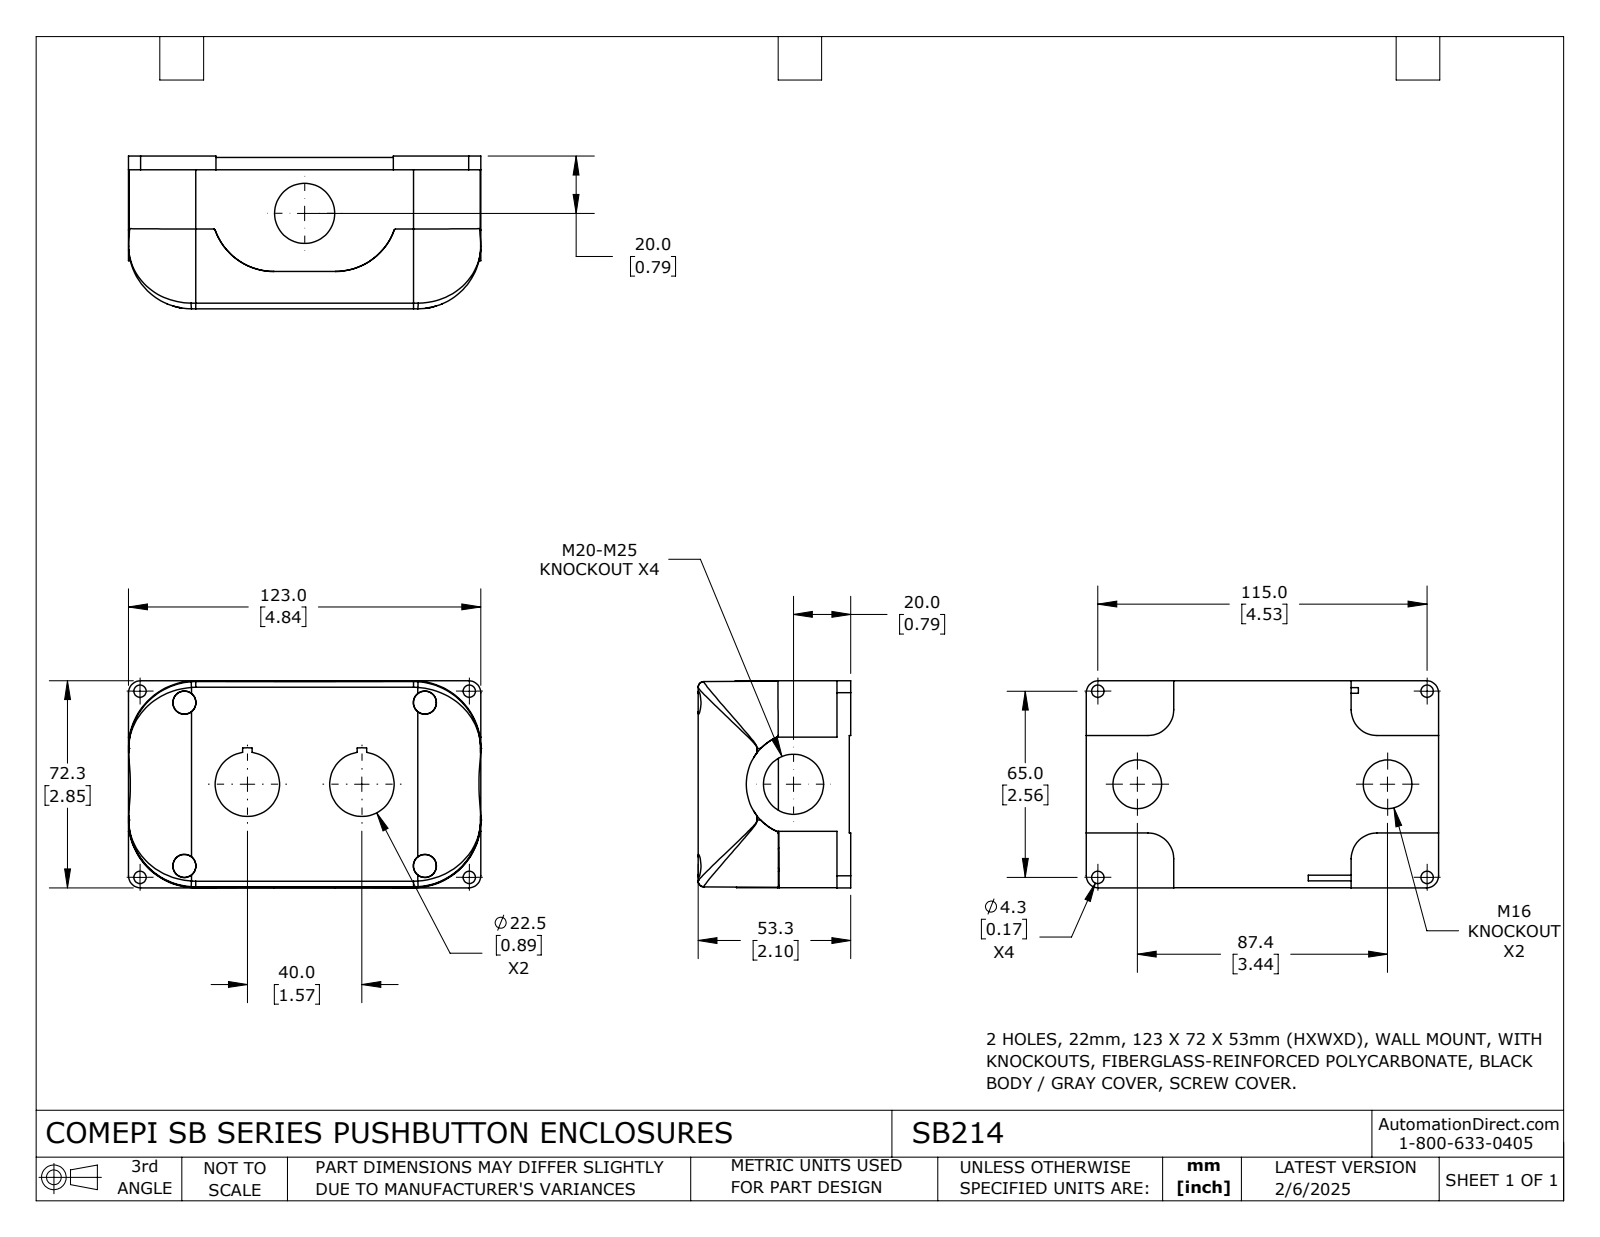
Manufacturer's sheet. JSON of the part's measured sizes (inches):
{"part_name": "SB214", "step_written_by": "SolidWorks 2024 (CONFIG_CONTROL_DESIGN)", "units": "inches", "bodies": {"solids": 2, "faces": 319, "planar": 157, "cylindrical": 74, "other": 88}, "overall_size": [4.843, 2.846, 2.098], "volume_in3": 15.59, "surface_area_in2": 106.2, "round_holes": [[0.169, 4], [0.669, 2], [0.827, 2]], "partial_cylinders_radius": [[0.035, 4], [0.079, 4], [0.157, 4], [0.354, 4], [0.38, 4], [0.866, 4], [0.93, 4], [0.787, 2]], "face_to_face_distances": [0.098, 2.079, 1.98, 1.102, 0.976, 0.878, 0.02, 0.118, 0.996, 2.098], "hole_center_spacings": [1.39, 4.185, 2.559, 4.528, 5.201, 3.441]}
